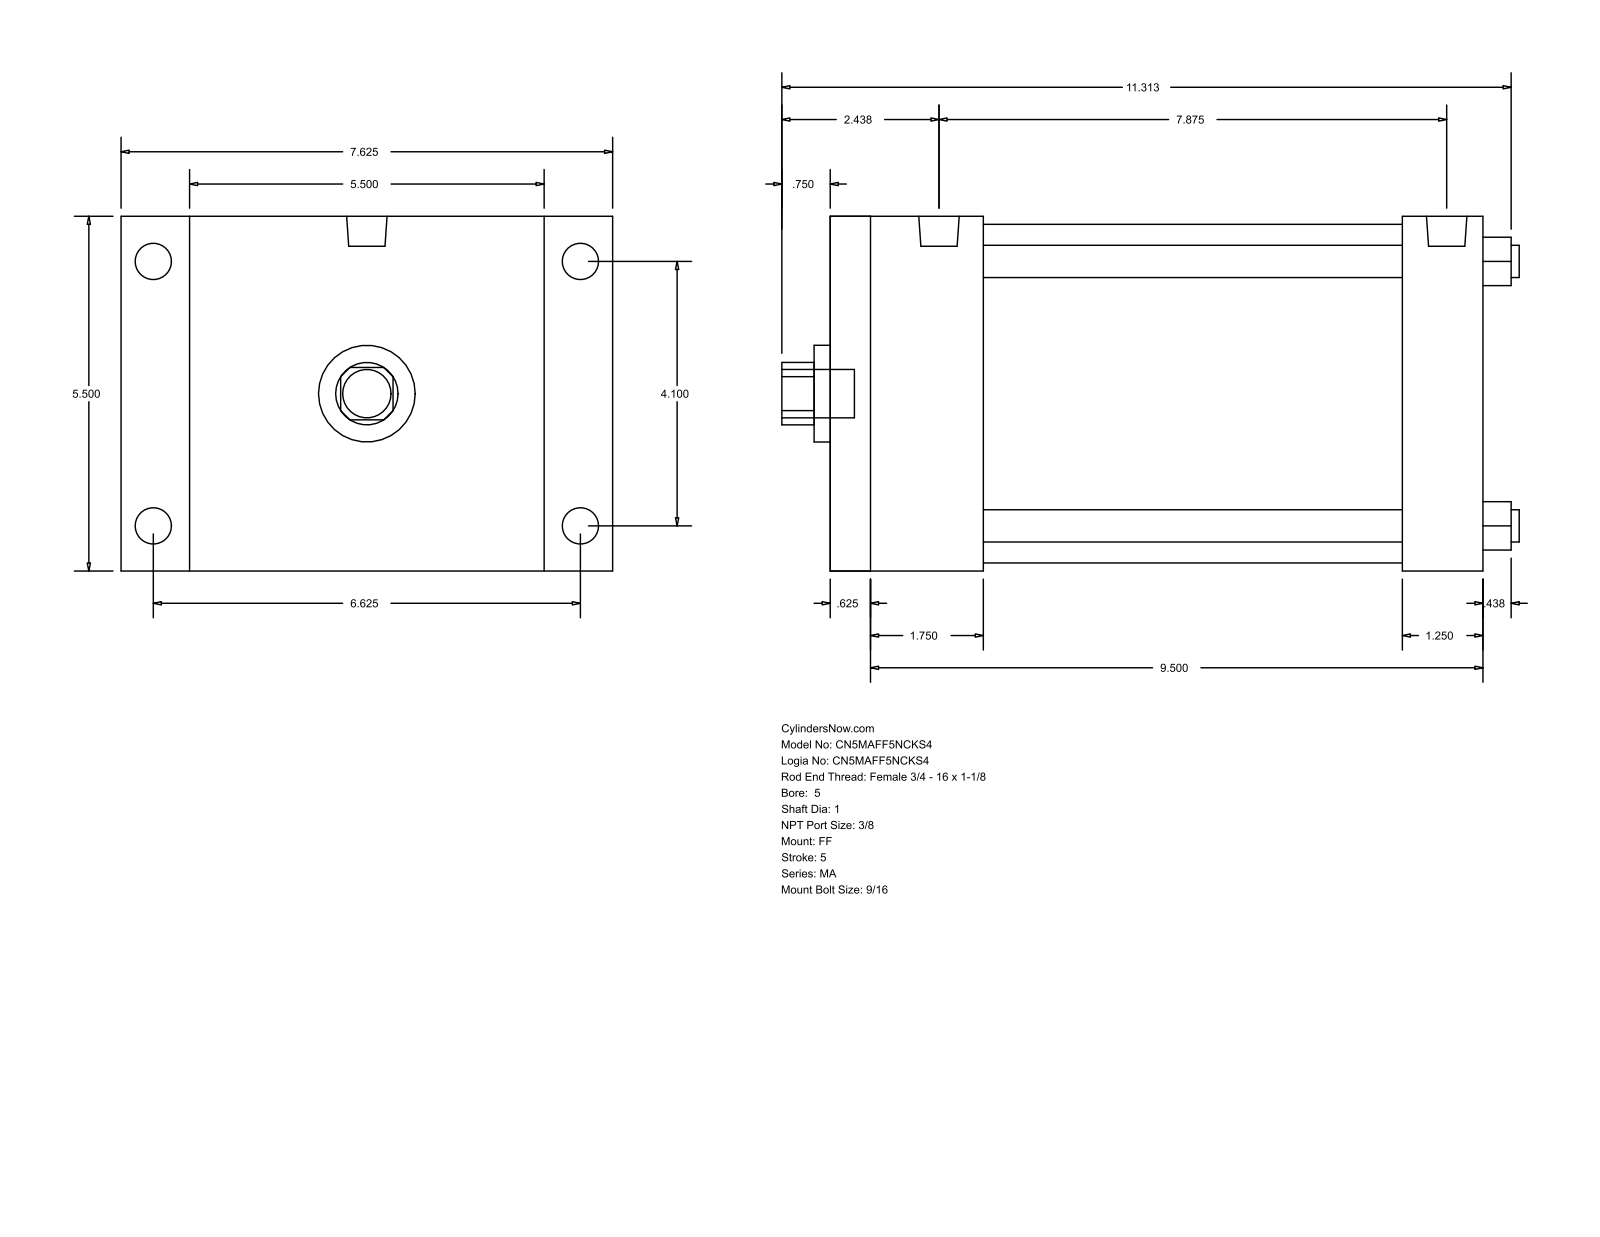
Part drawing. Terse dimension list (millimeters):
name: MA_FF__0500_1
written by: GSSL Pune (CONFIG_CONTROL_DESIGN)
unit: mm
bodies: 0 solids, 92 faces (64 planar, 28 cylindrical, 0 other)
size: 290.51 × 193.68 × 139.7
holes: 4× ⌀12.7, 1× ⌀25.4, 1× ⌀38.1, 1× ⌀133.35
bosses: 4× ⌀14.29, 4× ⌀11.11, 2× ⌀15.93, 1× ⌀19.05
rounds: 1× R12.29
face distances: 139.7, 257.18, 15.87, 241.31, 225.42, 209.55, 31.76, 60.33, 44.46, 165.09
hole spacings: 73.64, 104.14, 147.28
